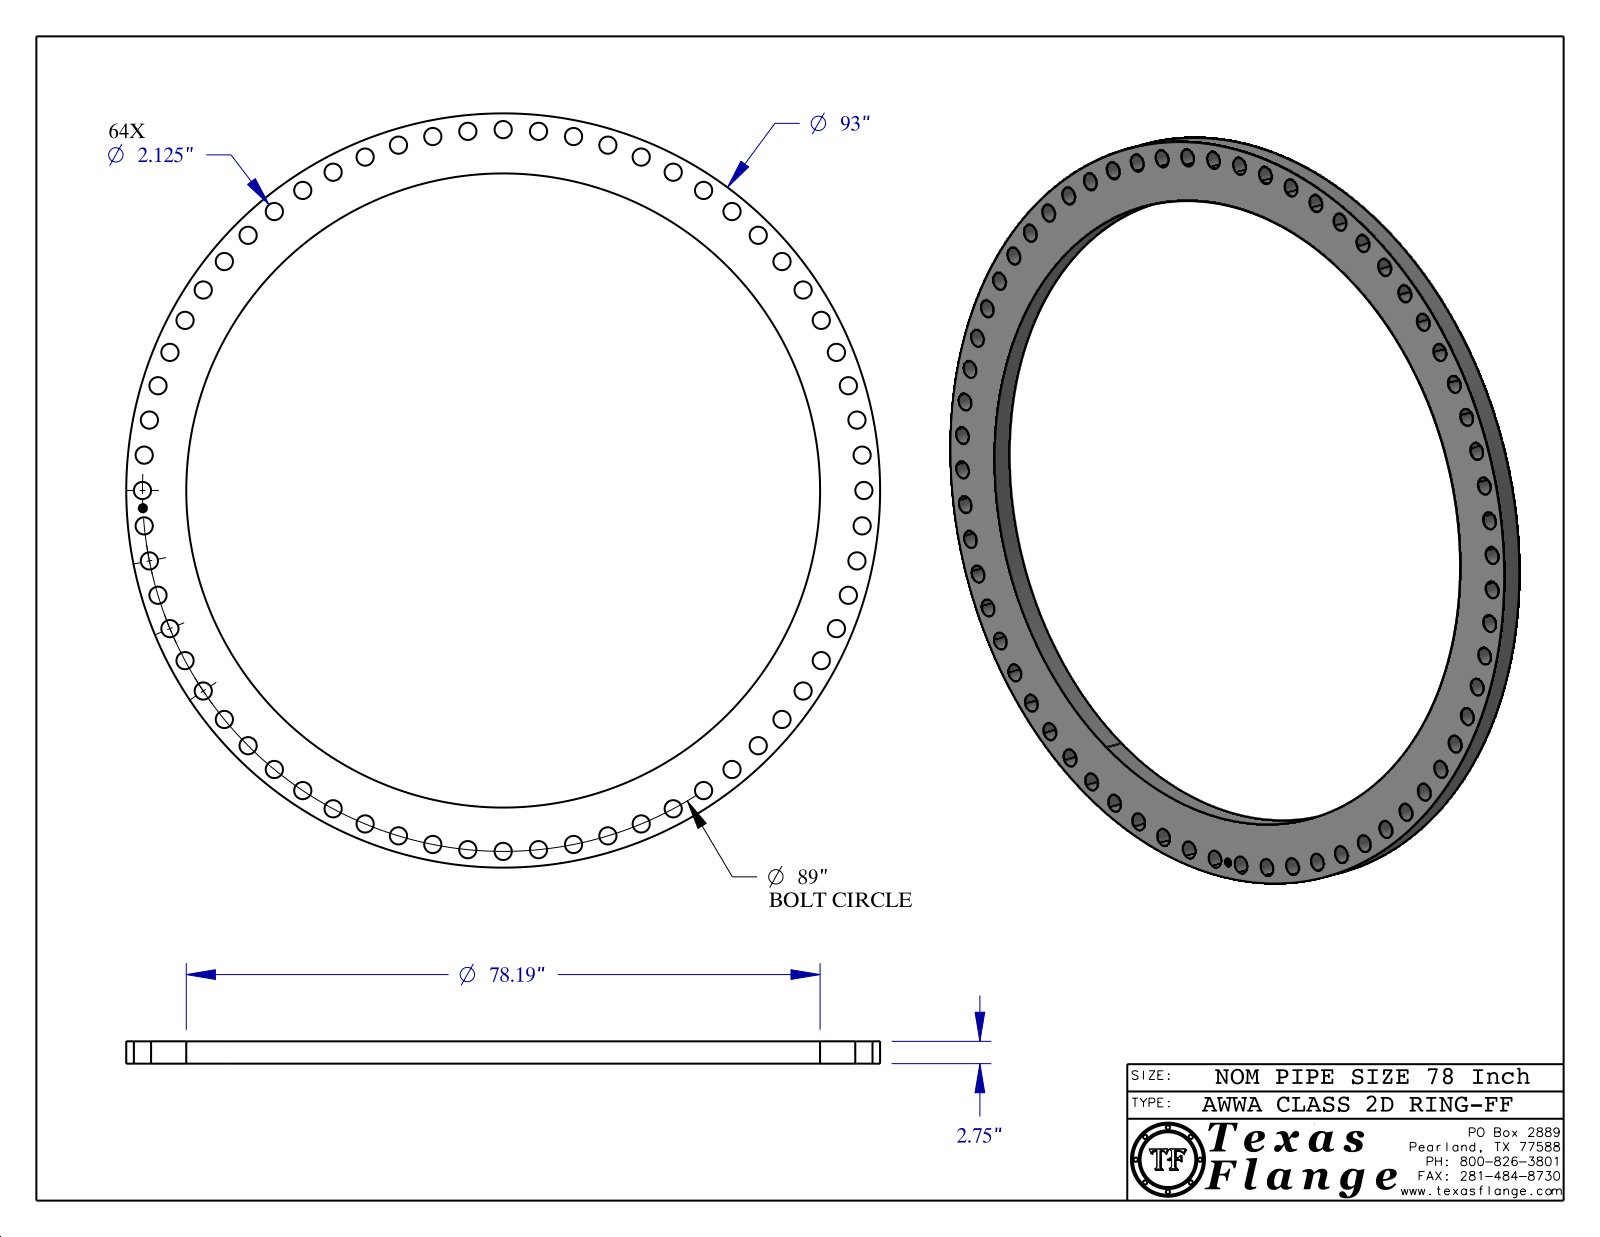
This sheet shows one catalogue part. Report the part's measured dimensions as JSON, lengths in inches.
{"part_name": "AWWA Class 2D-RING-FF", "step_written_by": "CATIA V5 STEP AP214 (AUTOMOTIVE_DESIGN)", "units": "inches", "bodies": {"solids": 1, "faces": 519, "planar": 367, "cylindrical": 152, "other": 0}, "overall_size": [93, 93, 2.75], "volume_in3": 4852, "surface_area_in2": 6183, "round_holes": [[2.125, 64], [1, 1], [78.19, 1]], "round_bosses_or_shafts": [[0.061, 8], [93, 1], [0.788, 1]], "face_to_face_distances": [2.75, 0.015, 2.735, 0.298, 0.292, 0.054, 0.193, 0.248, 0.044, 0.15], "hole_center_spacings": [4.367, 17.363, 44.5, 8.724, 13.059, 21.625, 25.835, 29.983]}
